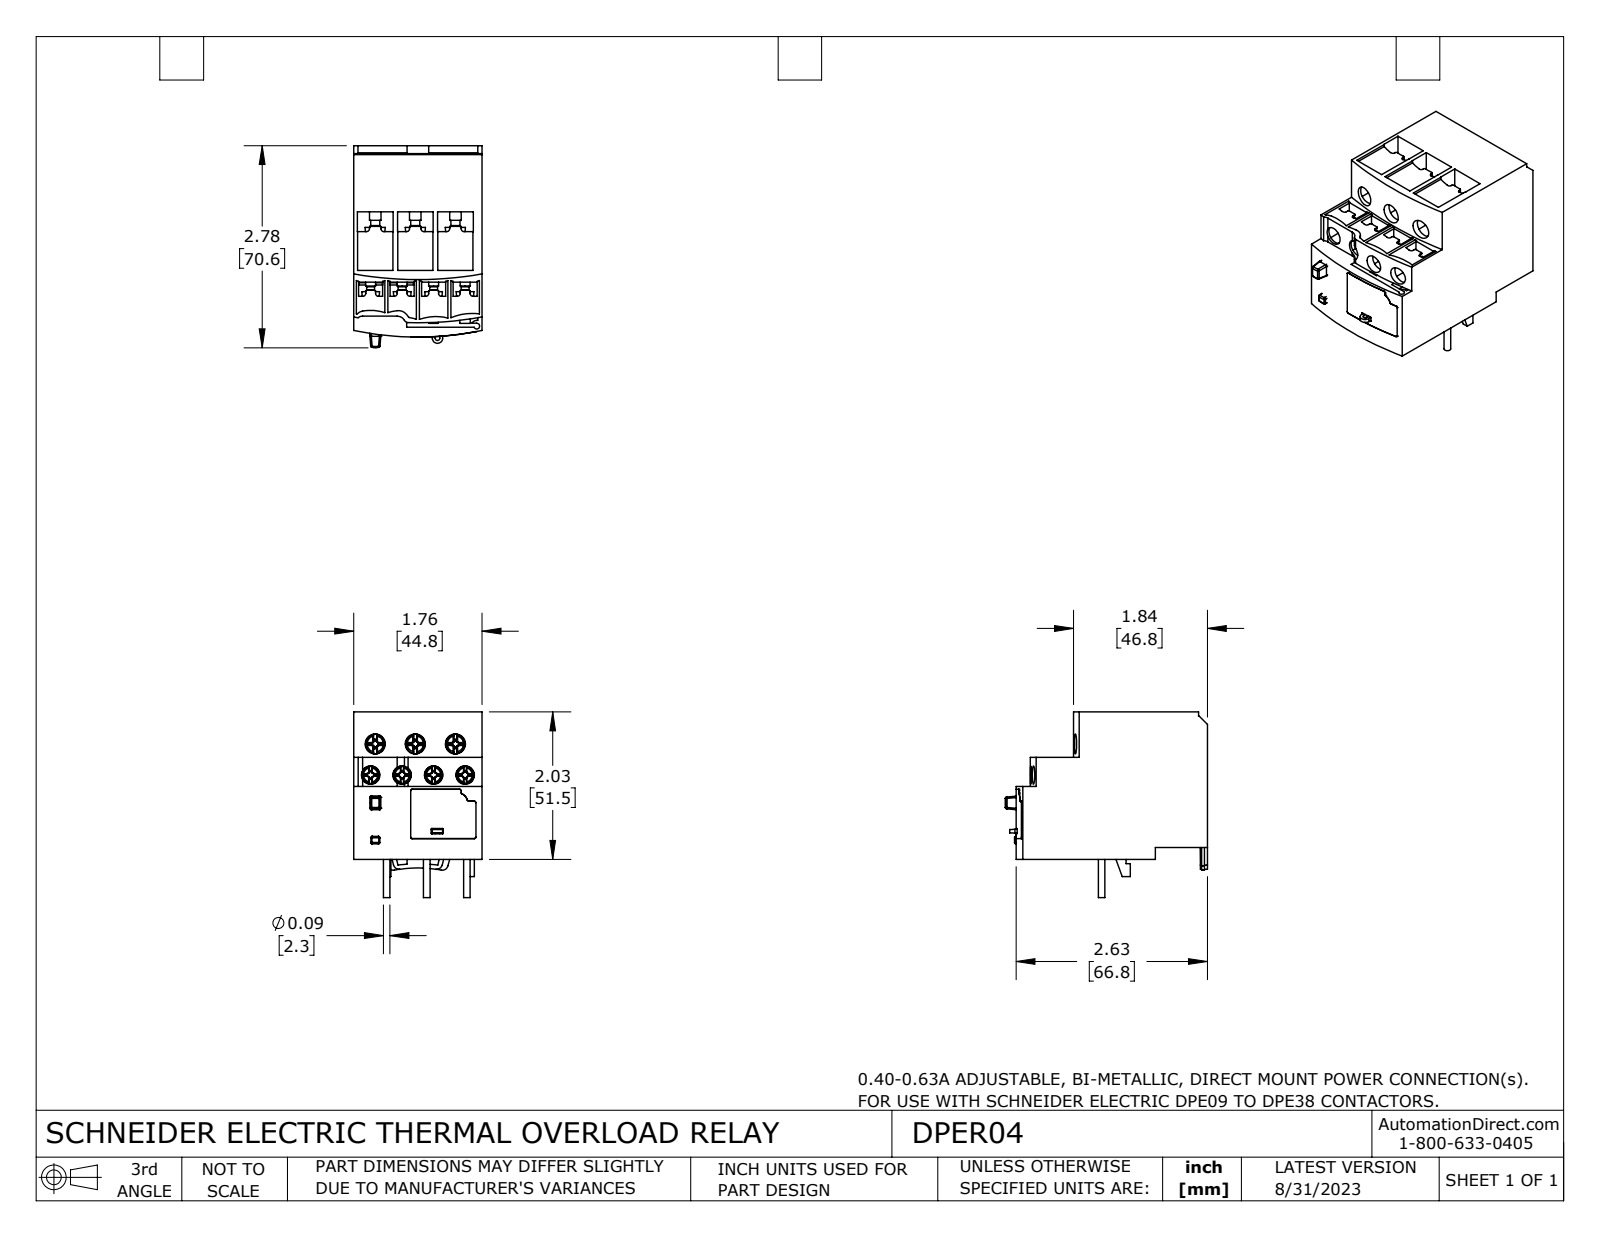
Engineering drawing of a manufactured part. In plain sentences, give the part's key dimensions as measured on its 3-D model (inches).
The part is named "DPER04". Its 3-D file was written by "SolidWorks 2021 (CONFIG_CONTROL_DESIGN)". It is 16 solids with 1212 faces: 676 planar, 269 cylindrical and 267 other. Overall it measures 2.778 by 2.553 by 1.764 inches. Its volume is 6.953 cubic inches and its surface area 47.15 square inches. Round holes: 4 of diameter 0.252, 3 of diameter 0.276, 2 of diameter 0.079, 2 of diameter 0.118, 1 of diameter 0.059, 1 of diameter 0.244. Round bosses or shafts: 12 of diameter 0.091, 4 of diameter 0.138, 4 of diameter 0.108, 3 of diameter 0.157, 3 of diameter 0.154, 3 of diameter 0.124, 1 of diameter 0.118, 1 of diameter 0.107. Partial cylindrical surfaces (rounded edges, fillets, slot ends): 52 of radius 0.02, 22 of radius 0.039, 19 of radius 0.004, 8 of radius 0.012, 6 of radius 0.008, 6 of radius 0.63, 4 of radius 0.079, 2 of radius 0.024. The main face-to-face distances are 1.764, 0.165, 2.028, 1.863, 0.909, 0.551, 0.618, 1.409, 1.245, 2.497. The hole center spacings are 0.433, 0.551, 0.866, 0.334, 0.381, 0.404, 0.422, 0.449.
